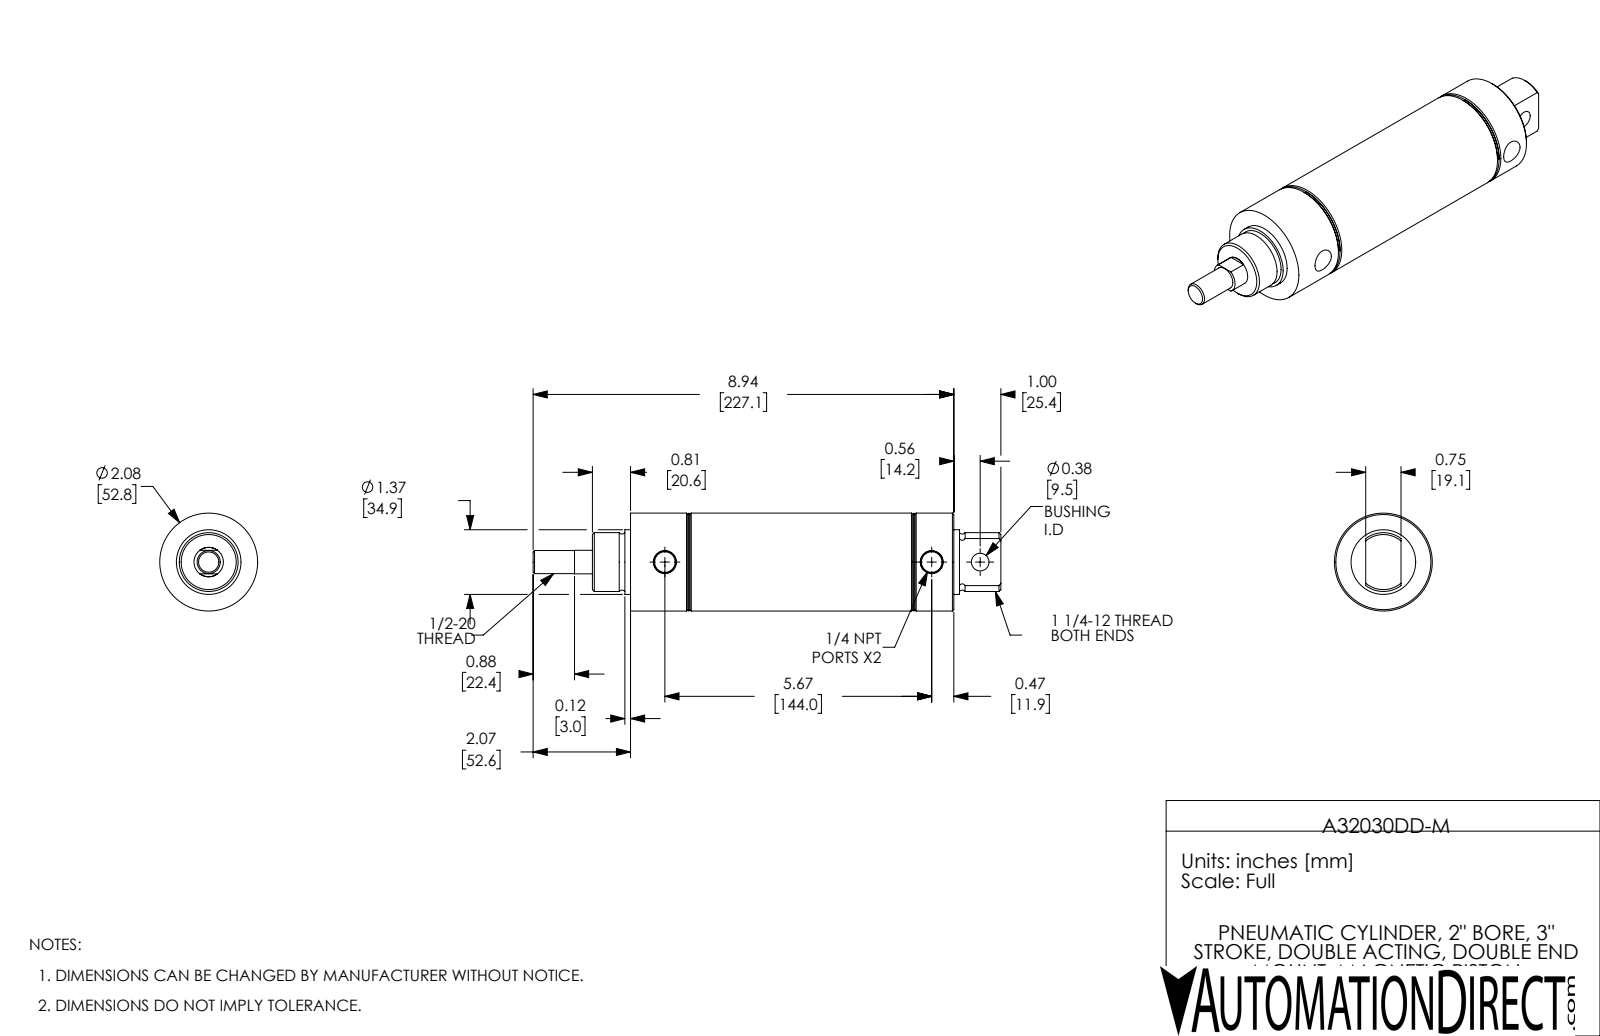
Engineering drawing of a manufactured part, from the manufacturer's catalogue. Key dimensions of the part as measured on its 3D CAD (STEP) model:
Part name (STEP PRODUCT): A32030DD-M-MainBody; A32030DD-M-Rod; A32030DD-M
STEP written by: SolidWorks 2017 (AUTOMOTIVE_DESIGN)
Units: inches
Bodies: 2 solids, 88 faces (20 planar, 30 cylindrical, 38 other)
Overall size (bounding box): 9.94 × 2.08 × 2.08
Volume: 16.67 in³ · Surface area: 116.6 in²
Round holes (diameter × count): ⌀0.438 ×2, ⌀0.375 ×1, ⌀0.625 ×1, ⌀2 ×1
Round bosses / shafts (diameter × count): ⌀2.08 ×1, ⌀1.373 ×1, ⌀1.25 ×1, ⌀0.491 ×1
Main face-to-face distances: 1.685, 5.185, 0.5, 3.5, 0.5, 3.5, 3, 5.185, 4.685, 1.685
Hole centre spacings: 1.03, 5.67, 6.7
